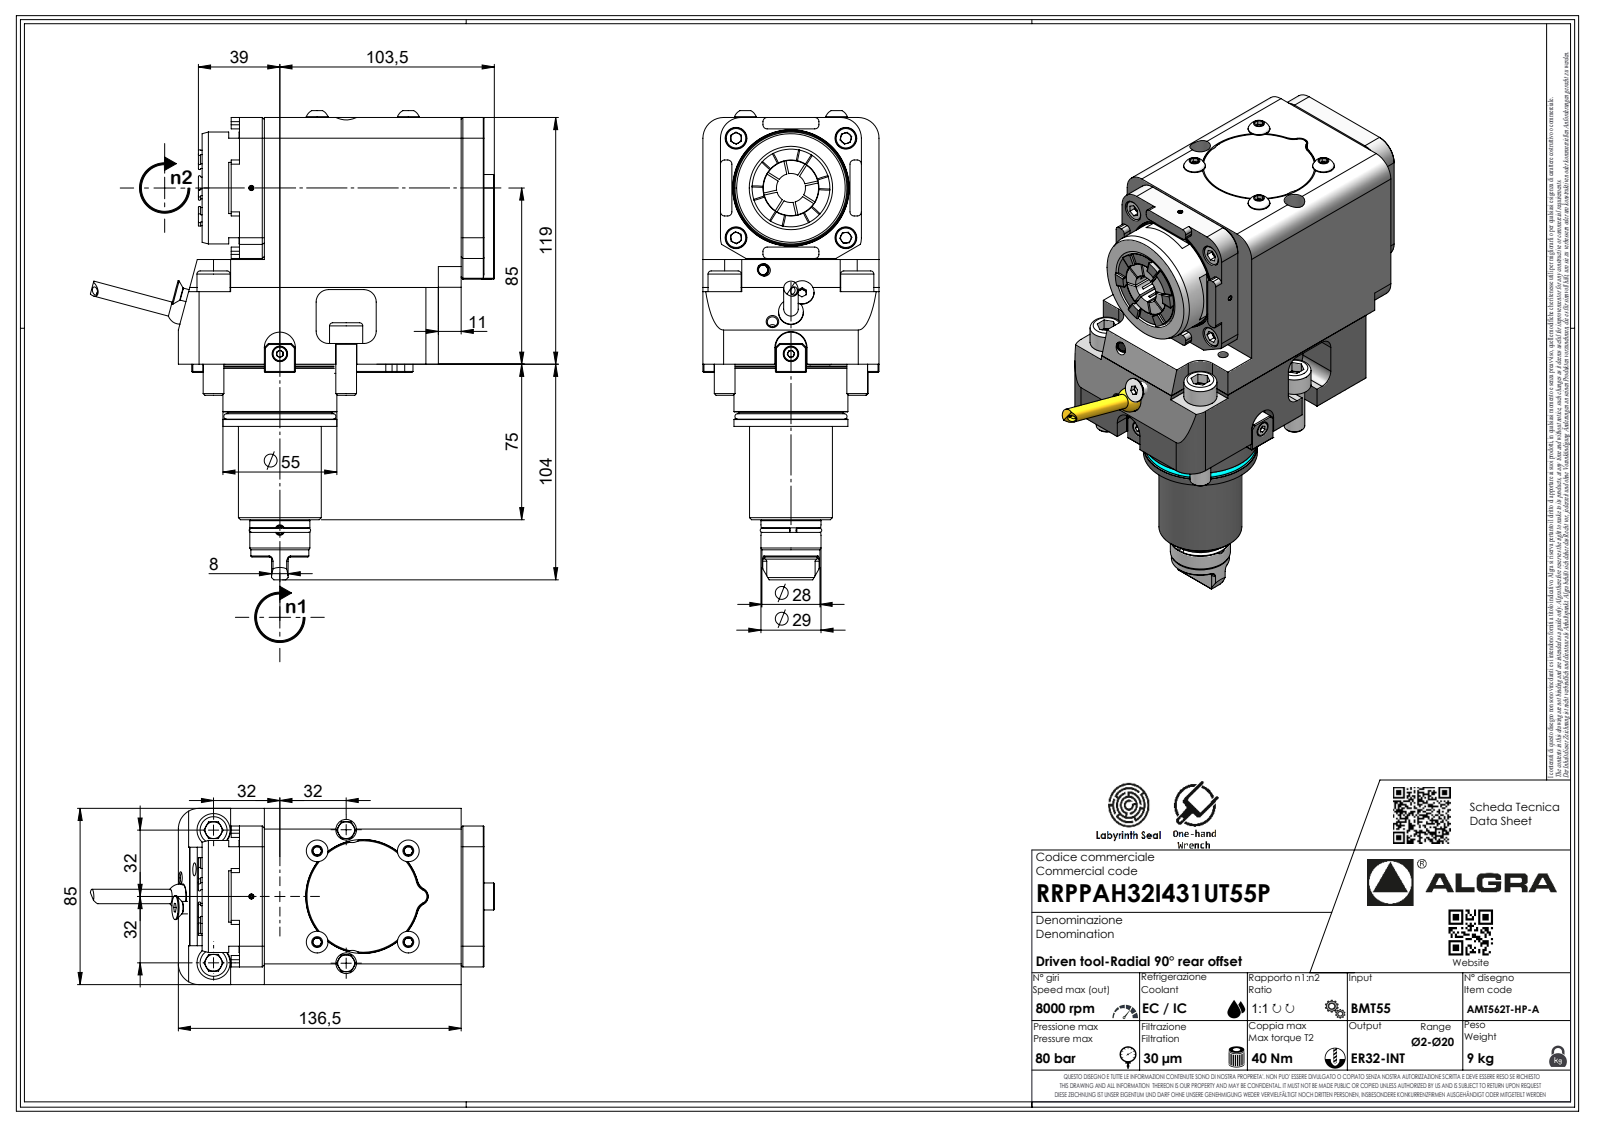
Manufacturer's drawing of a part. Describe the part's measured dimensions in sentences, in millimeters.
The part is named "RRPPAH32I431UT55P". Its 3-D file was written by "SolidWorks 2023 (AUTOMOTIVE_DESIGN)". It is 1 solid with 686 faces: 416 planar, 108 cylindrical and 162 other. Overall it measures 226.3 by 194.45 by 85 millimeters. Its volume is 1 375 000 cubic millimeters and its surface area 96 650 square millimeters. Round holes: 1 of diameter 2.1, 1 of diameter 4. Round bosses or shafts: 4 of diameter 10.5, 4 of diameter 10, 2 of diameter 16, 1 of diameter 55, 1 of diameter 54.6, 1 of diameter 54, 1 of diameter 50.2, 1 of diameter 40. Partial cylindrical surfaces (rounded edges, fillets, slot ends): 23 of radius 2, 10 of radius 10, 7 of radius 0.33, 7 of radius 0.52, 7 of radius 3.7, 4 of radius 4, 2 of radius 1, 2 of radius 8.25. The main face-to-face distances are 85, 119, 11, 21.5, 30, 10.5, 68, 68.5, 50.5, 8.5.
